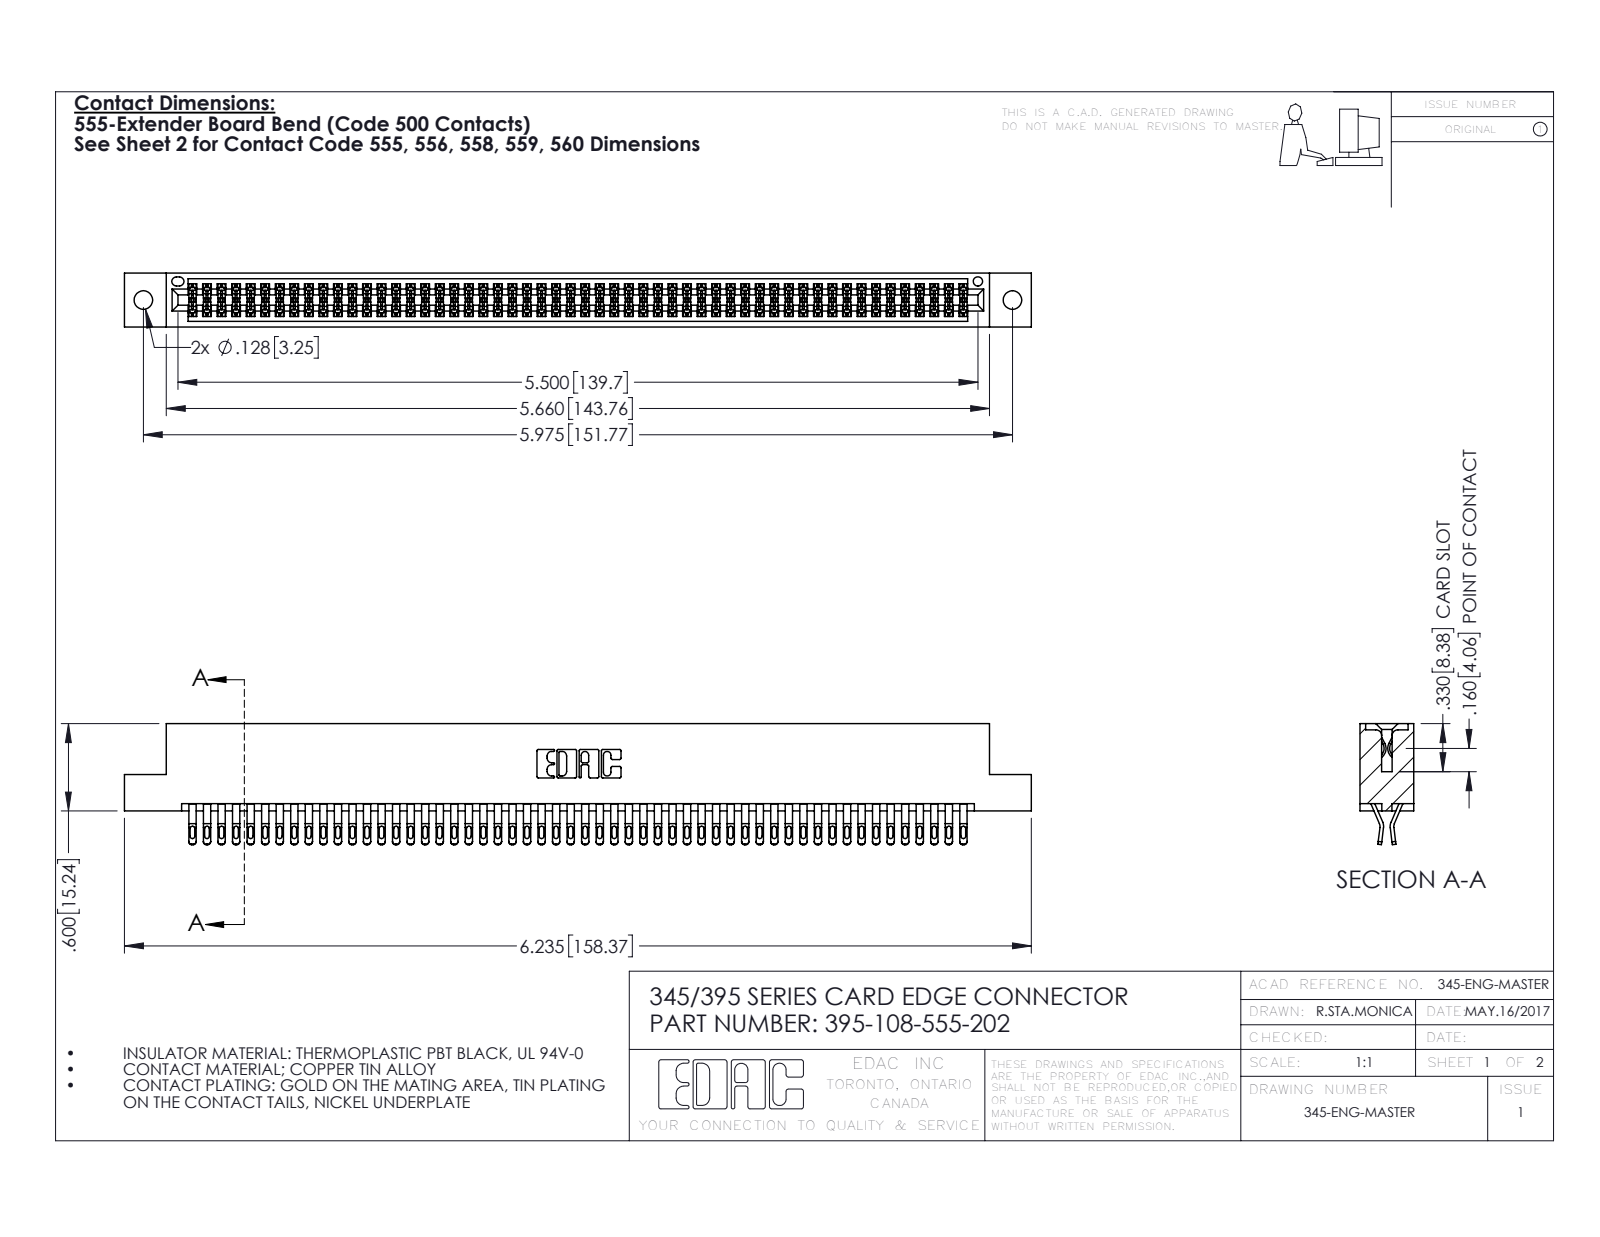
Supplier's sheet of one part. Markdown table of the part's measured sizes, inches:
| quantity | value |
| --- | --- |
| part name | 345-292-001_555 Tail; 345 Part_Flush Mounting Lugs - 0.128 Dia; 395-108-555-202 |
| STEP written by | SolidWorks 2016 (CONFIG_CONTROL_DESIGN) |
| units | inches |
| bodies | 109 solids, 6174 faces (3428 planar, 2746 cylindrical, 0 other) |
| overall size | 6.235 × 0.832 × 0.37 |
| volume | 0.962 in³ |
| surface area | 37.76 in² |
| round holes (diameter × count) | 0.128 × 2, 0.064 × 1 |
| partial cylindrical surfaces (radius × count) | 0.016 × 270, 0.02 × 216, 0.006 × 162, 0.01 × 22, 0.007 × 6, 0.031 × 6, 0.026 × 3, 0.01 × 2 |
| main face-to-face distances | 0.298, 0.072, 0.025, 0.37, 0.2, 0.098, 0.272, 0.225, 0.175, 0.149 |
| hole center spacings | 0.27, 5.739, 5.975 |
